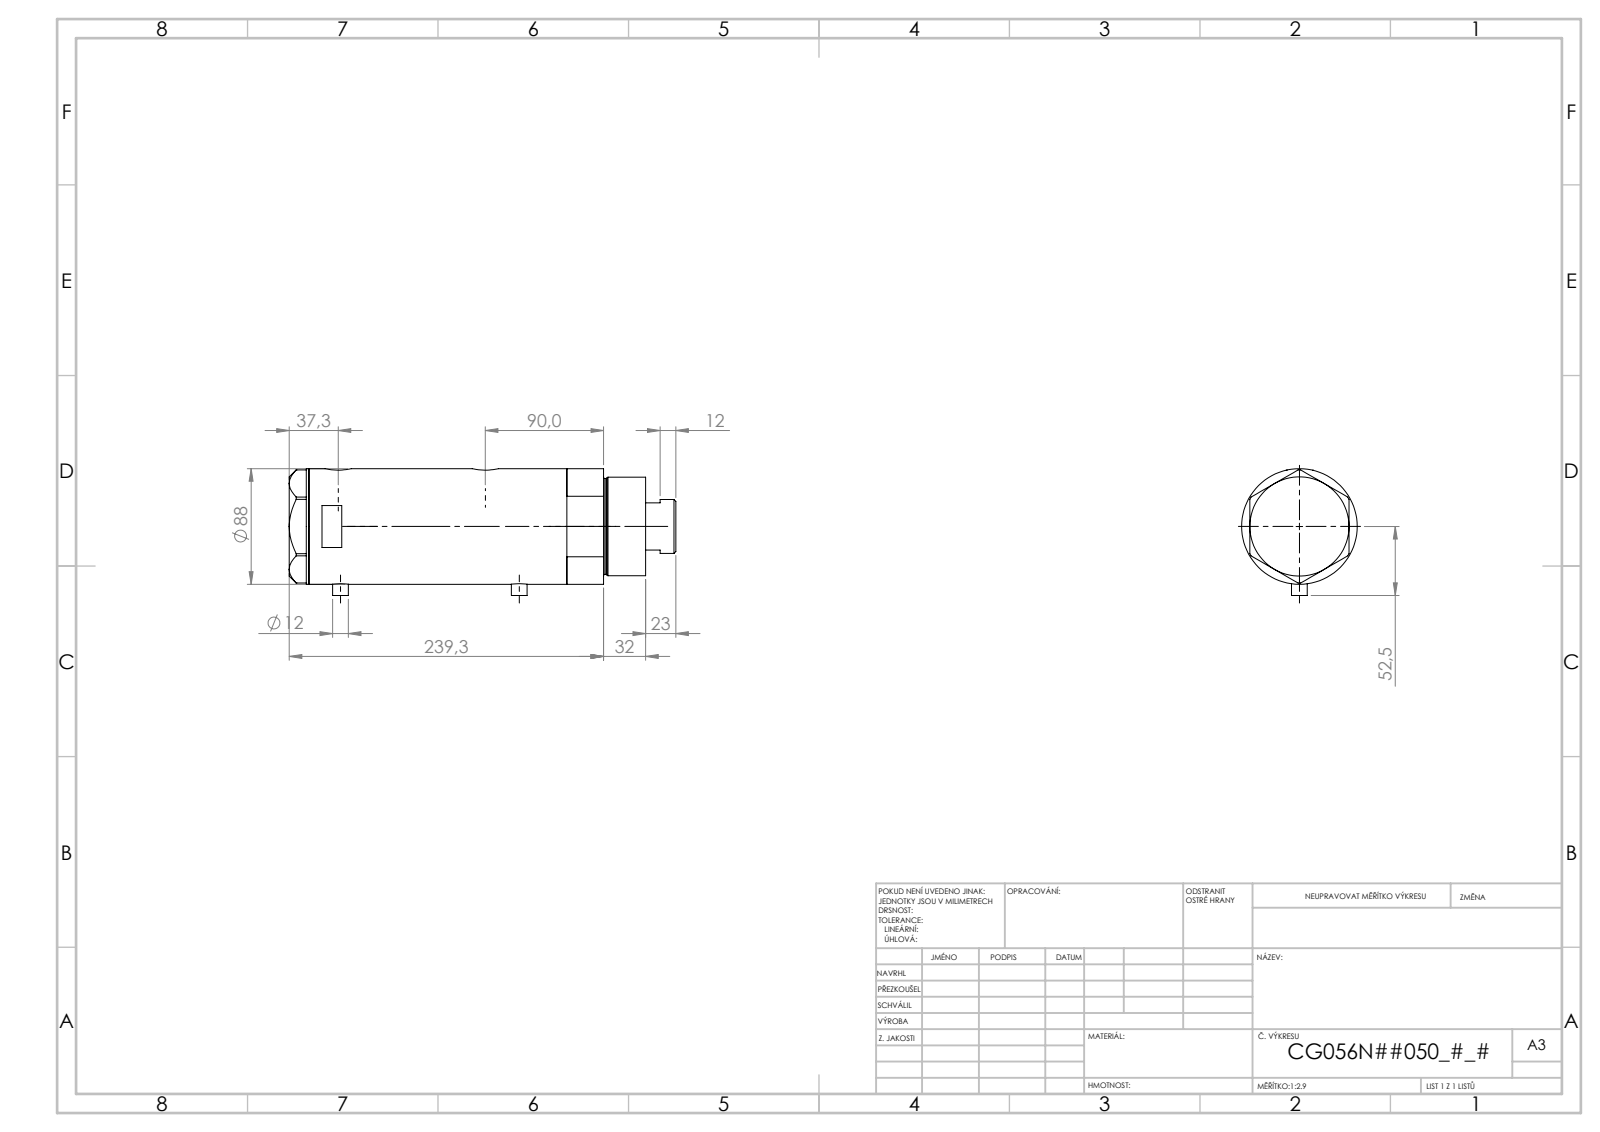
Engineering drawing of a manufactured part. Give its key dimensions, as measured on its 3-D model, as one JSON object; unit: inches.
{"part_name": "V270CG_MIDDLE; V270CG_FRONT; V270CG_VC; V270CG_BACK", "step_written_by": "SolidWorks 2019 (CONFIG_CONTROL_DESIGN)", "units": "inches", "bodies": {"solids": 4, "faces": 126, "planar": 53, "cylindrical": 53, "other": 20}, "overall_size": [10.806, 3.508, 3.465], "volume_in3": 86.17, "surface_area_in2": 324.7, "round_holes": [[0.197, 2], [0.492, 2], [0.518, 2], [0.787, 2], [0.571, 1], [1.654, 1], [1.713, 1], [2.205, 1], [2.362, 1], [3.15, 1]], "round_bosses_or_shafts": [[0.472, 2], [3.465, 1], [2.953, 1], [2.874, 1], [1.614, 1]], "face_to_face_distances": [4.898, 1.024, 3.874, 0.591, 1.614, 5.488, 9.31, 9.9, 8.286, 4.412], "hole_center_spacings": [0.067, 1.016, 3.949, 4.016, 4.965, 5.031]}
